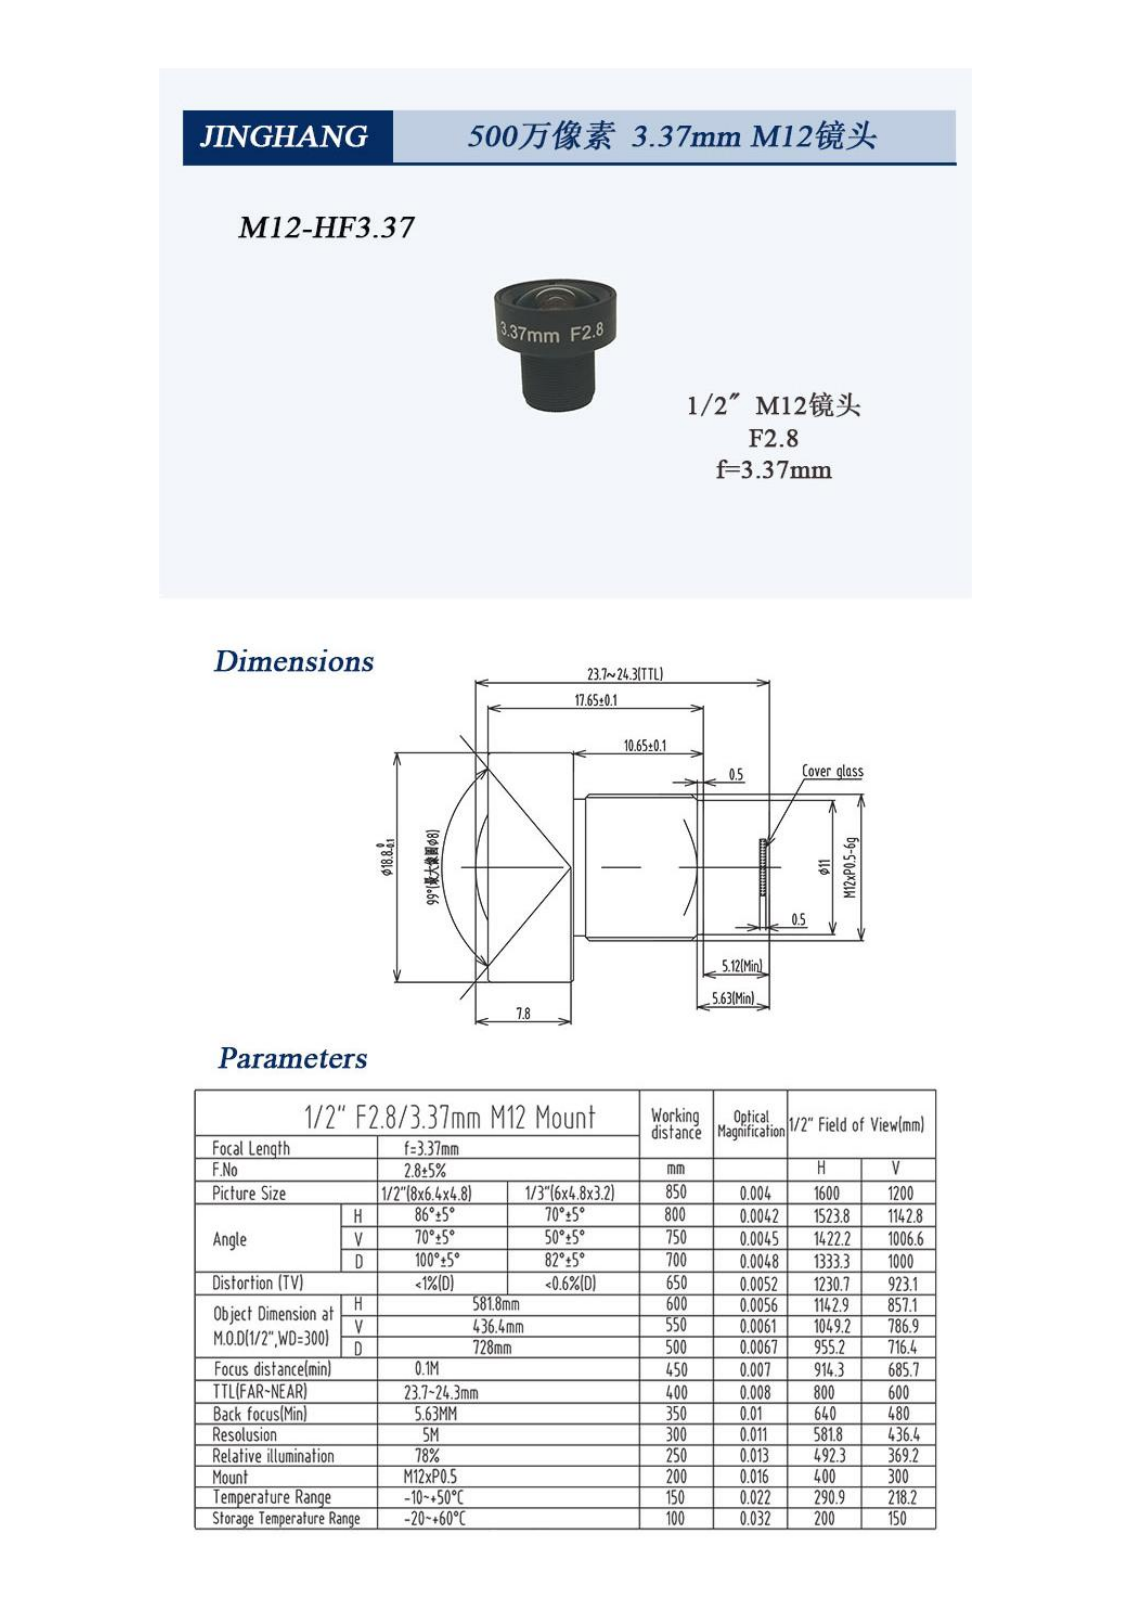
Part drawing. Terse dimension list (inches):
name: FS0305A-200
written by: PRO/ENGINEER BY PARAMETRIC TECHNOLOGY CORPORATION, 2010370 (CONFIG_CONTROL_DESIGN)
unit: in
bodies: 1 solid, 93 faces (7 planar, 45 cylindrical, 41 other)
size: 0.74 × 0.74 × 0.735
volume: 0.179 in³; area: 2.554 in²
holes: 1× ⌀0.315, 1× ⌀0.524, 1× ⌀0.664
bosses: 1× ⌀0.74, 1× ⌀0.472, 1× ⌀0.441, 1× ⌀0.433
face distances: 0.263, 0.682, 0.419, 0.013, 0.276, 0.695, 0.666, 0.654, 0.391, 0.029
